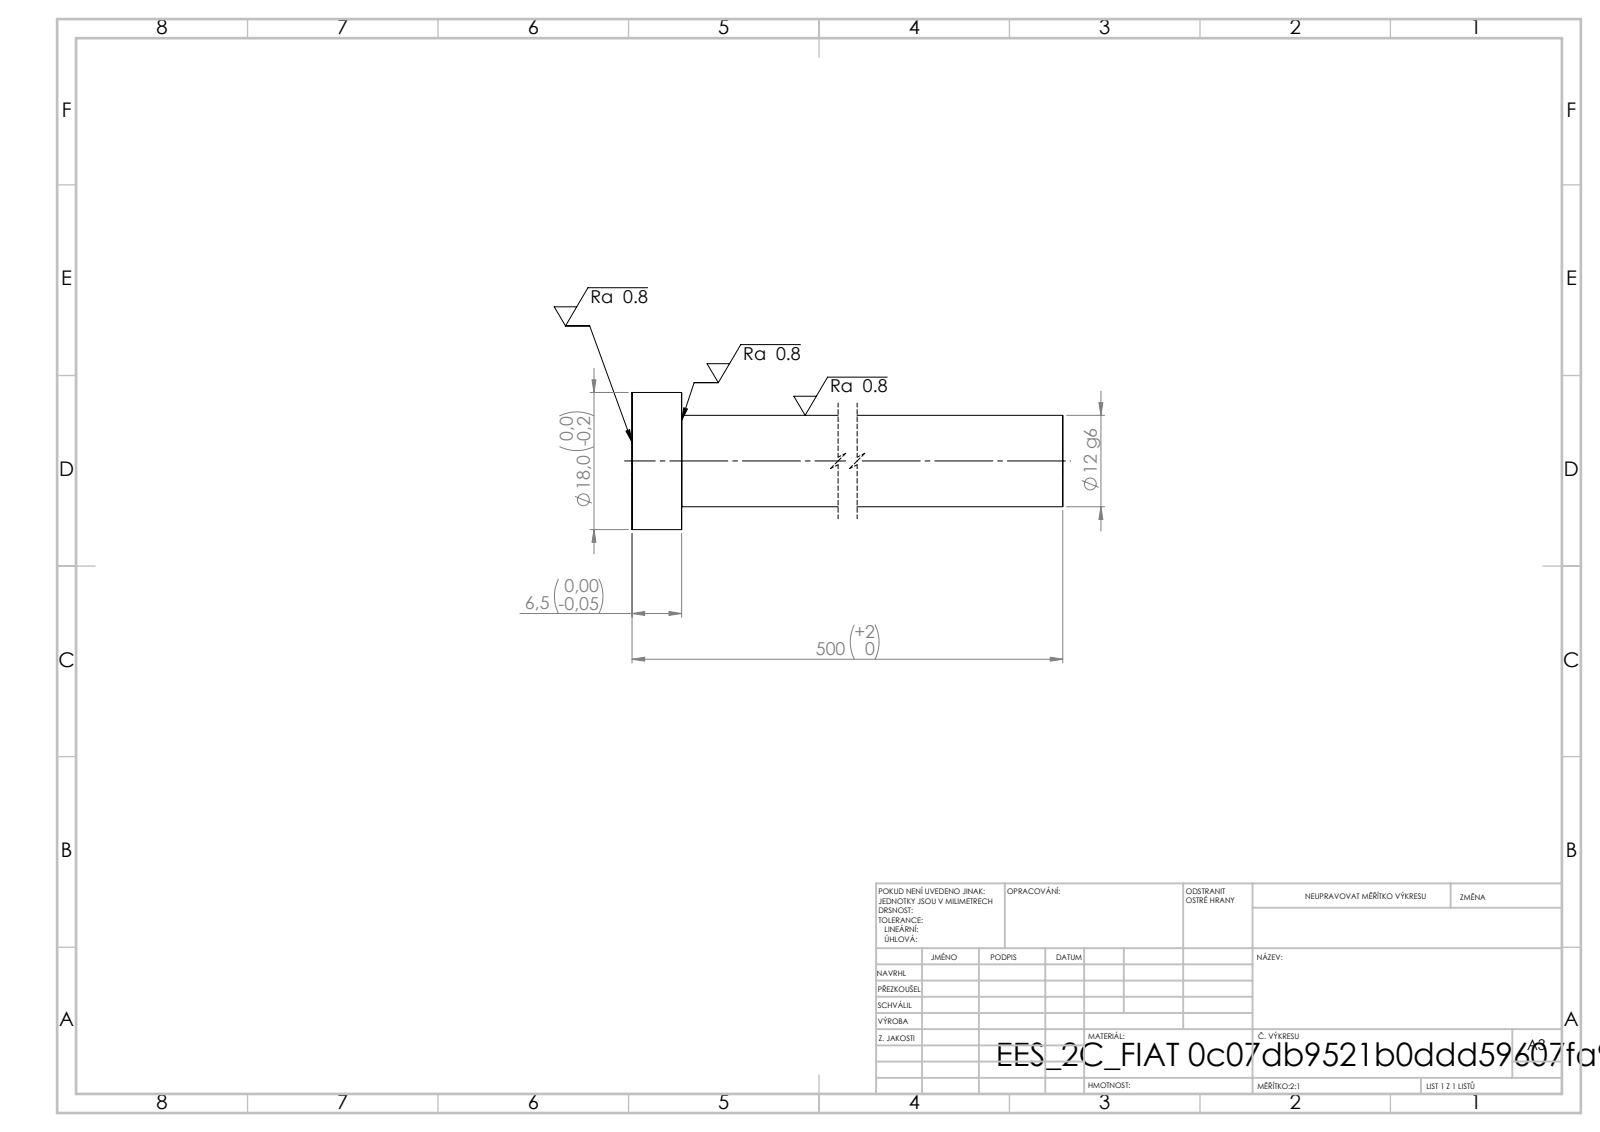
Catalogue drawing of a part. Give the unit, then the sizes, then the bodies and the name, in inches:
Units: inches
Overall size (bounding box): 19.685 × 0.709 × 0.709
Round bosses / shafts (diameter × count): ⌀0.709 ×1, ⌀0.472 ×1
Main face-to-face distances: 0.256, 19.685, 19.429
Volume: 3.507 in³ · Surface area: 30.2 in²
Bodies: 1 solid, 7 faces (3 planar, 4 cylindrical, 0 other)
STEP written by: SolidWorks 2019 (CONFIG_CONTROL_DESIGN)
